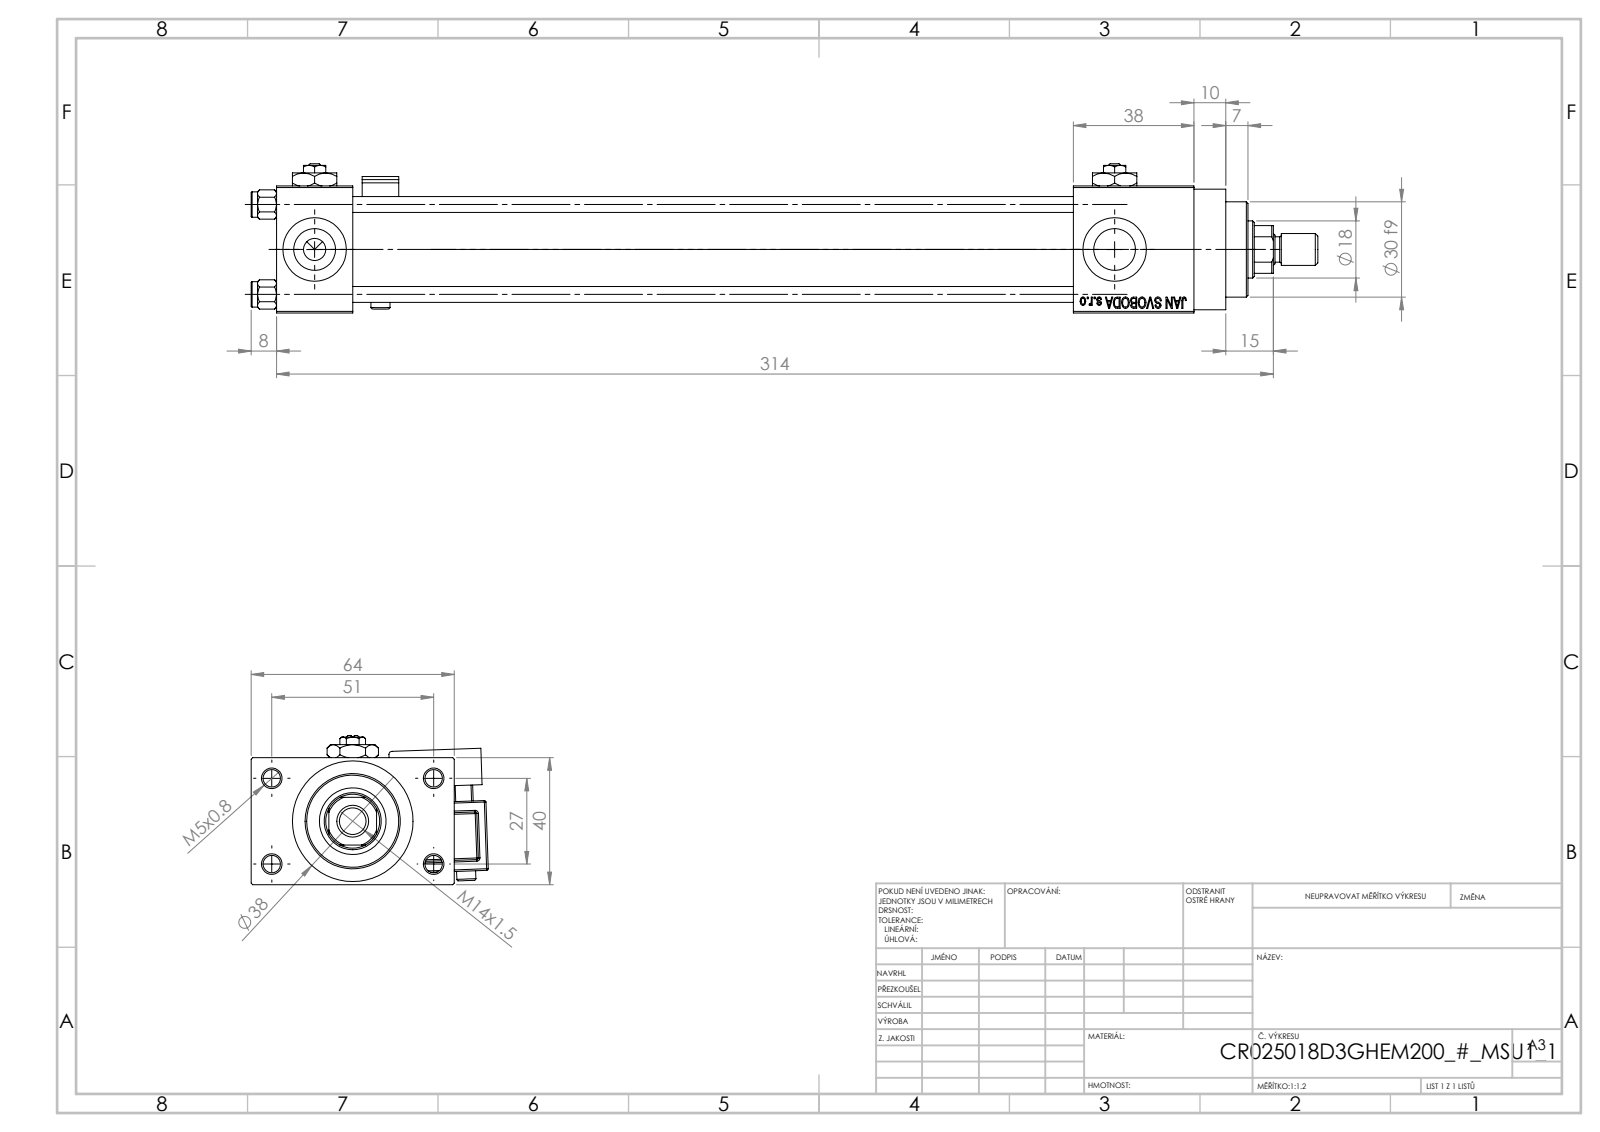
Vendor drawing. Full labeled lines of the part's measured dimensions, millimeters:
Part name (STEP PRODUCT): V215CR_MSU; V215CR_D_Body; ROD_END_E; V215CR_D_TYCINKA (+4 more)
STEP written by: SolidWorks 2019 (CONFIG_CONTROL_DESIGN)
Units: millimetres
Bodies: 15 solids, 1291 faces (576 planar, 131 cylindrical, 584 other)
Overall size (bounding box): 336 × 74.7 × 47
Volume: 306 964 mm³ · Surface area: 126 101 mm²
Round holes (diameter × count): ⌀20 ×5, ⌀5 ×4, ⌀5.5 ×4, ⌀13.16 ×4, ⌀7 ×3, ⌀8.5 ×1, ⌀18 ×1, ⌀21 ×1, ⌀25 ×1, ⌀30 ×1
Round bosses / shafts (diameter × count): ⌀8 ×5, ⌀38 ×1, ⌀31 ×1, ⌀10 ×1, ⌀6 ×1
Partial cylindrical surfaces — rounded edges, fillets, slot ends (radius × count): R0.5 ×24, R1 ×1, R2.5 ×1, R4 ×1, R8.5 ×1
Main face-to-face distances: 40, 24, 12, 227, 251, 52, 38, 289, 265, 64
Hole centre spacings: 11.37, 20.01, 28.3, 28.85, 29.89, 39.66, 48.34, 27
